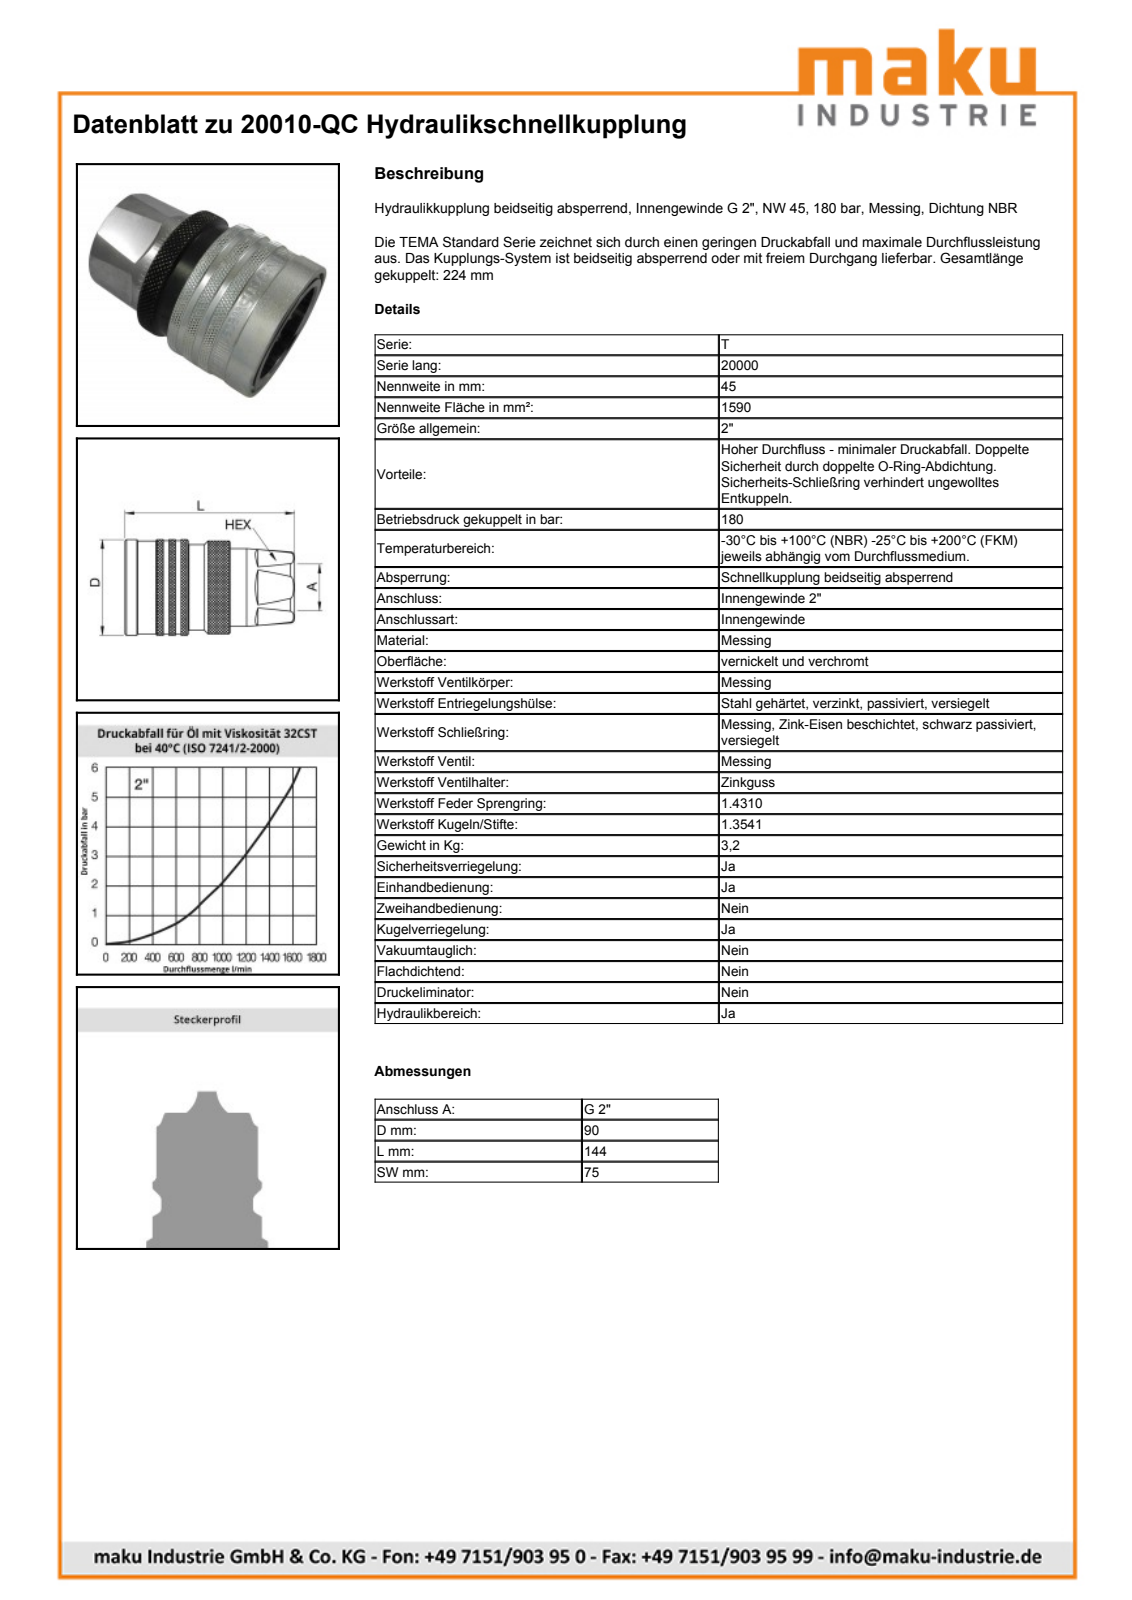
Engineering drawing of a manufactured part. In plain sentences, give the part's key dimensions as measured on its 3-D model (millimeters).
The part is named "20010-QC". Its 3-D file was written by "SolidWorks 2009 (AUTOMOTIVE_DESIGN)". It is 1 solid with 142 faces: 34 planar, 44 cylindrical and 64 other. Overall it measures 143.5 by 90 by 90 millimeters. Its volume is 568 479 cubic millimeters and its surface area 89 996 square millimeters. Round holes: 1 of diameter 45, 1 of diameter 56.65, 1 of diameter 60, 1 of diameter 60.5, 1 of diameter 65, 1 of diameter 65.3, 1 of diameter 70, 1 of diameter 82.5. Round bosses or shafts: 1 of diameter 90, 1 of diameter 88.5, 1 of diameter 88, 1 of diameter 85, 1 of diameter 84, 1 of diameter 83.5, 1 of diameter 77, 1 of diameter 48. The main face-to-face distances are 75, 27, 116.5, 143.5, 22, 4, 90.4, 82.55, 55.55, 60.95.
